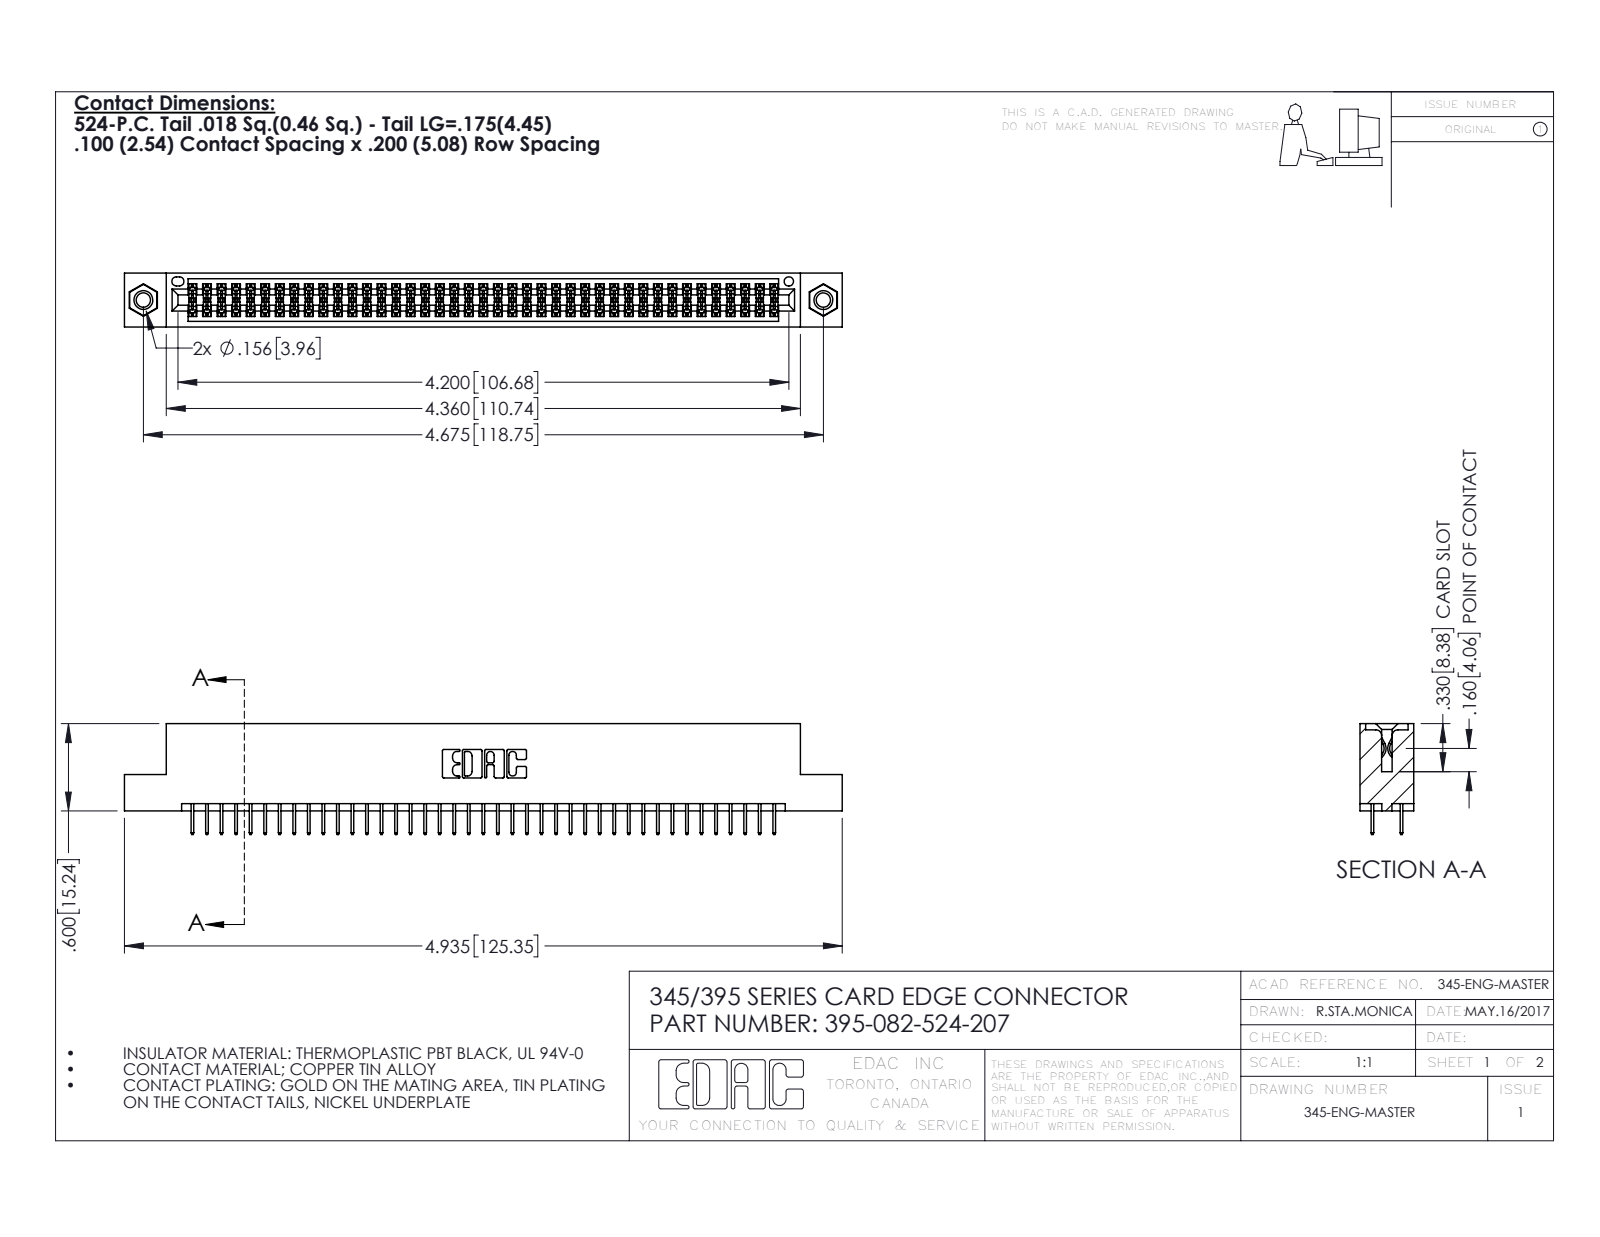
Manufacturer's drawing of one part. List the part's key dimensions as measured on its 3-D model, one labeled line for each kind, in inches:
Part name (STEP PRODUCT): 345-250-001_345-250-005-103; 345-292-001_345-293-124; 395-082-524-207; 345 Part_Flush Mounting Lugs - 0.156 Dia-TI
STEP written by: SolidWorks 2016 (CONFIG_CONTROL_DESIGN)
Units: inches
Bodies: 85 solids, 4614 faces (3310 planar, 1288 cylindrical, 16 other)
Overall size (bounding box): 4.935 × 0.762 × 0.37
Volume: 0.734 in³ · Surface area: 27.07 in²
Round holes (diameter × count): ⌀0.098 ×2, ⌀0.125 ×2, ⌀0.156 ×2, ⌀0.064 ×1
Round bosses / shafts (diameter × count): ⌀0.155 ×2
Partial cylindrical surfaces — rounded edges, fillets, slot ends (radius × count): R0.006 ×123, R0.01 ×22, R0.007 ×6, R0.031 ×6, R0.026 ×3, R0.014 ×2, R0.019 ×2, R0.022 ×2
Main face-to-face distances: 0.072, 0.298, 0.2, 0.37, 0.098, 0.272, 0.025, 0.225, 0.072, 0.175
Hole centre spacings: 0.27, 4.439, 4.675
